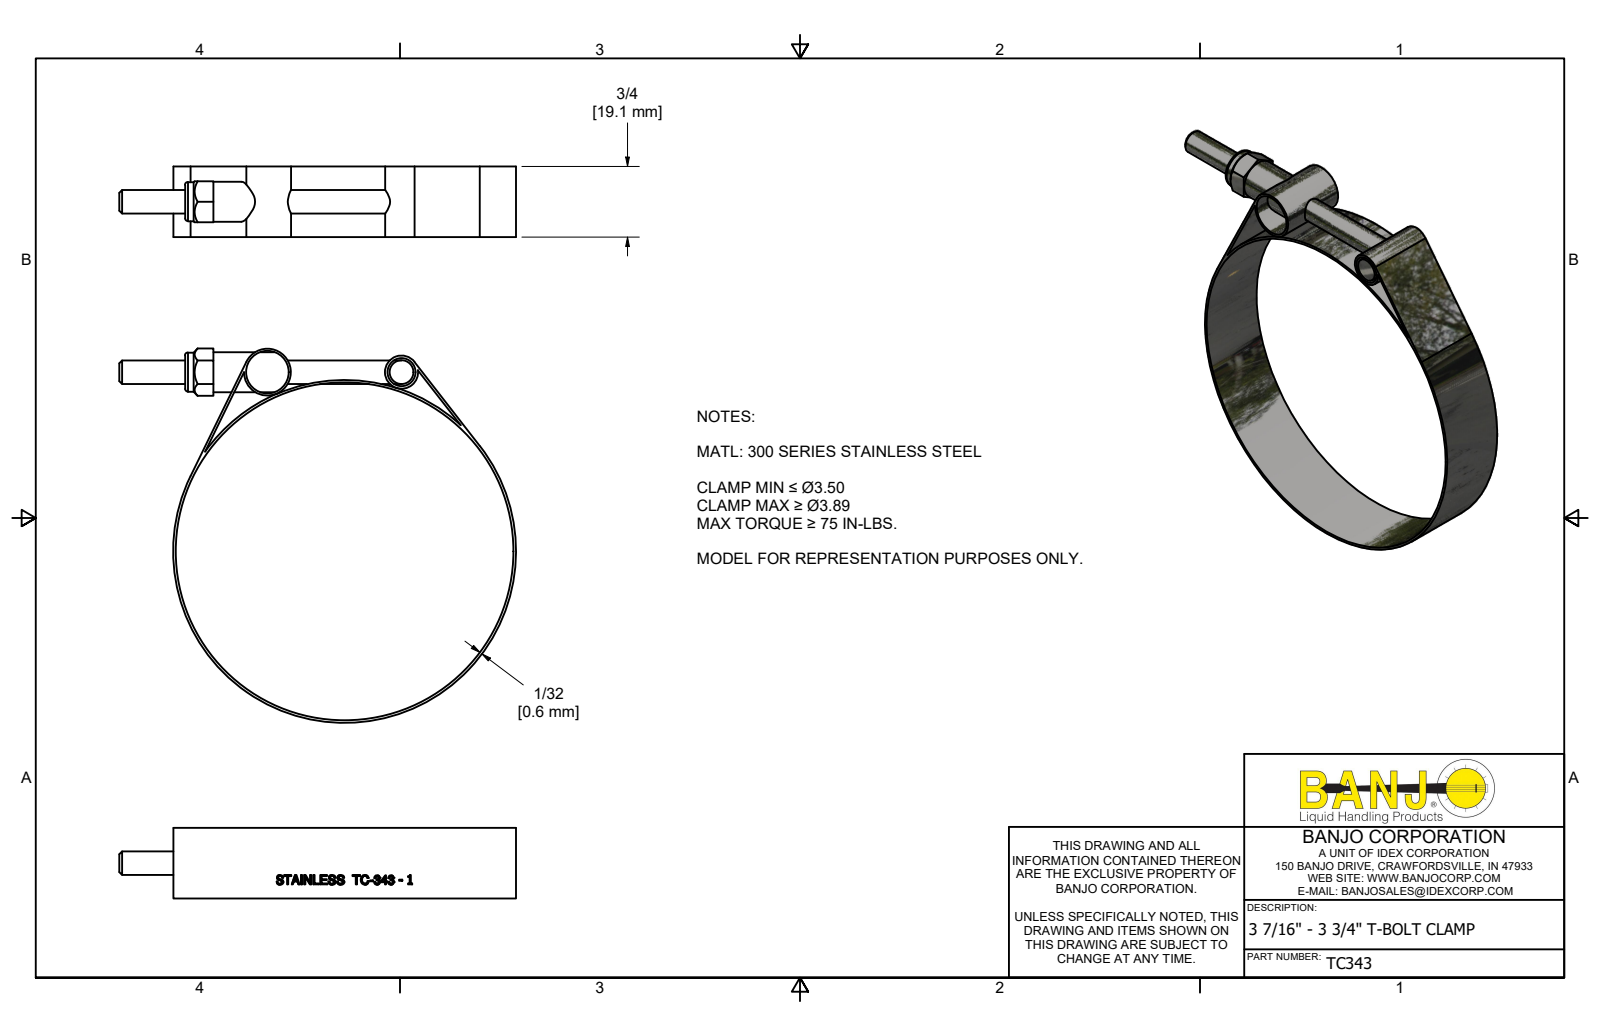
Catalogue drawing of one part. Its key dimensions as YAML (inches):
part_name: "TC343"
step_written_by: "Autodesk Inventor 2022 (AUTOMOTIVE_DESIGN)"
units: inches
bodies: {solids: 1, faces: 252, planar: 114, cylindrical: 39, other: 99}
overall_size: [4.214, 3.972, 0.75]
volume: 0.565
surface_area: 26.56
round_holes:
  - {diameter: 0.3, count: 1}
  - {diameter: 0.45, count: 1}
  - {diameter: 3.59, count: 1}
round_bosses_or_shafts:
  - {diameter: 0.25, count: 2}
  - {diameter: 3.64, count: 1}
  - {diameter: 0.5, count: 1}
  - {diameter: 0.425, count: 1}
  - {diameter: 0.415, count: 1}
  - {diameter: 0.35, count: 1}
partial_cylinders:
  - {radius: 1.815, count: 1}
face_to_face_distances: [0.026, 0.025, 0.75, 0.157, 0.592, 0.435, 0.435, 0.7, 1, 0.3]
hole_center_spacings: [1.425, 1.995, 2.07]
